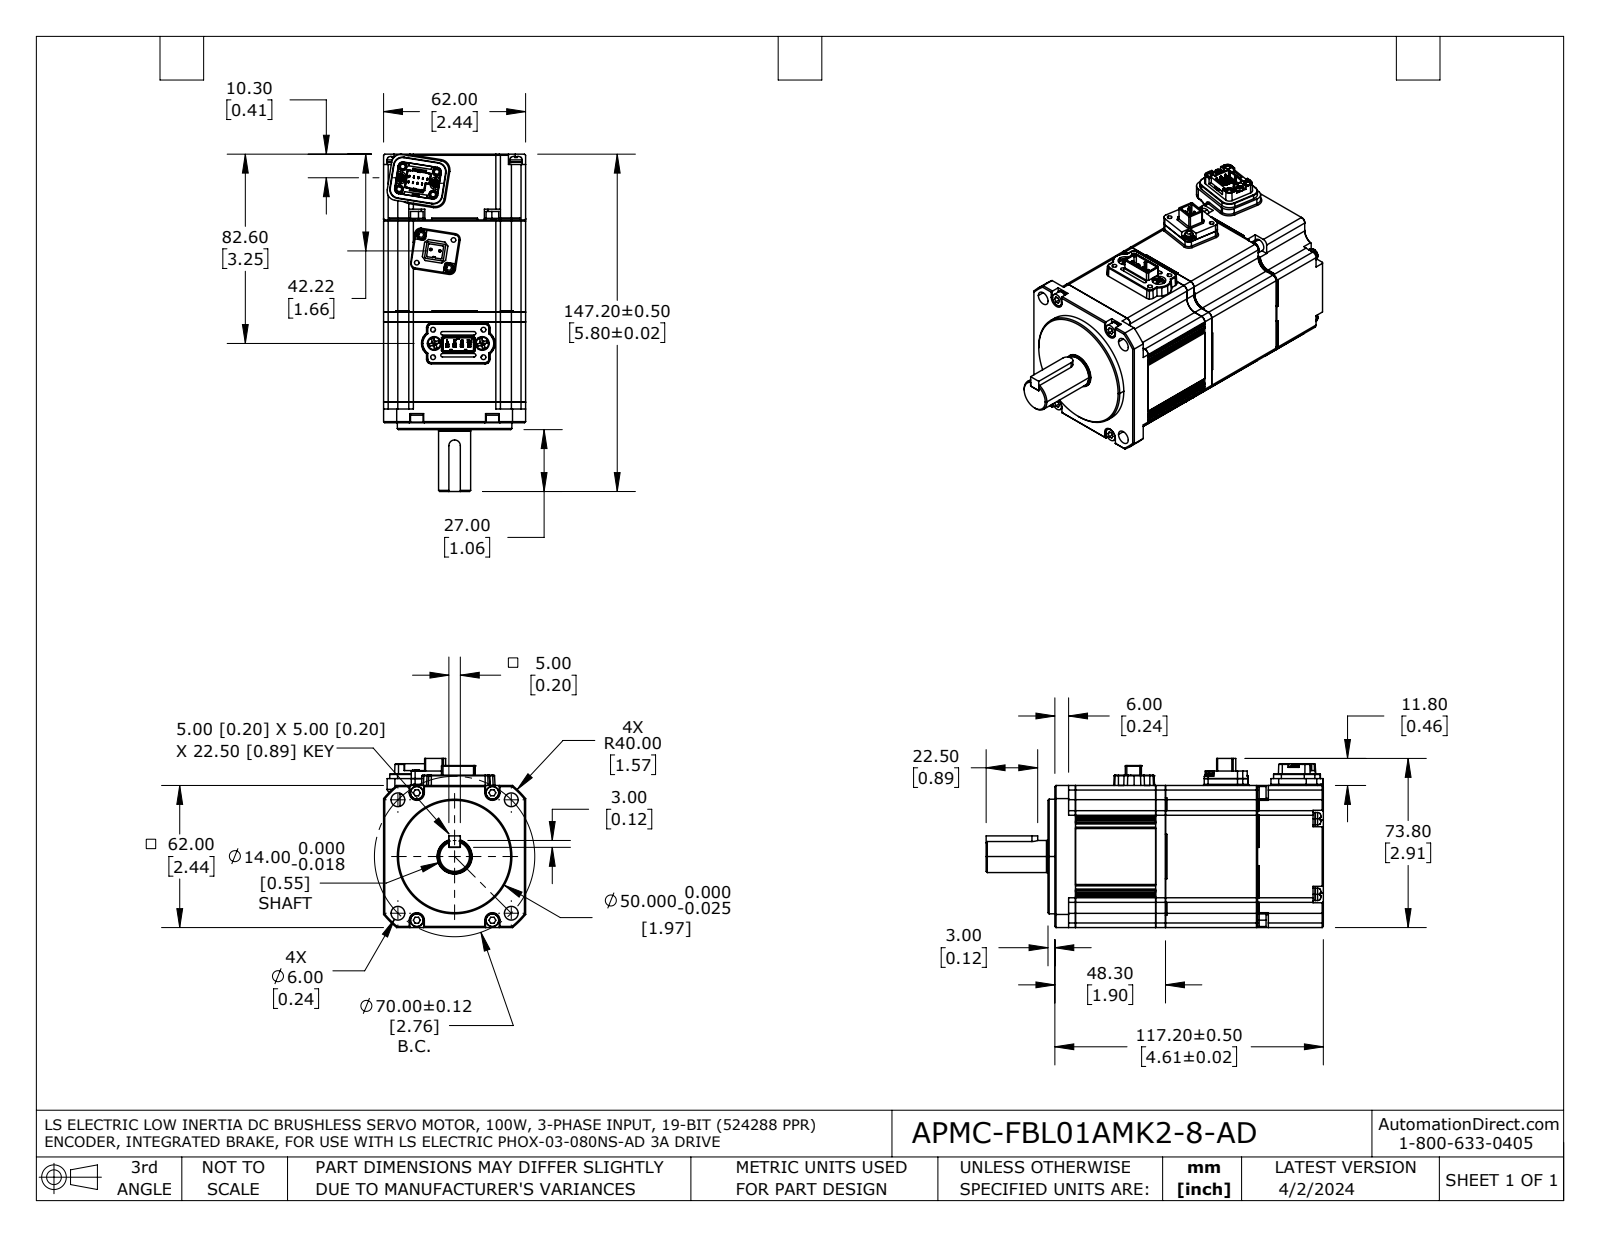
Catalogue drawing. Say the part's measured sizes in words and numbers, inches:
The part is named "APMC-FBL01AMK2-8-AD". Its 3-D file was written by "SolidWorks 2021 (AUTOMOTIVE_DESIGN)". It is 51 solids with 2196 faces: 1289 planar, 673 cylindrical and 234 other. Overall it measures 5.795 by 2.906 by 2.441 inches. Its volume is 25.14 cubic inches and its surface area 148.8 square inches. Round holes: 10 of diameter 0.083, 8 of diameter 0.138, 6 of diameter 0.118, 6 of diameter 0.236, 4 of diameter 0.079, 4 of diameter 0.122, 2 of diameter 0.039, 1 of diameter 0.13, 1 of diameter 0.134, 1 of diameter 0.512, 1 of diameter 0.602. Round bosses or shafts: 6 of diameter 0.213, 4 of diameter 0.22, 4 of diameter 0.217, 4 of diameter 0.118, 2 of diameter 0.165, 2 of diameter 0.142, 2 of diameter 0.138, 2 of diameter 0.087. Partial cylindrical surfaces (rounded edges, fillets, slot ends): 20 of radius 0.008, 20 of radius 0.012, 14 of radius 0.039, 12 of radius 0.079, 9 of radius 0.006, 8 of radius 0.118, 7 of radius 0.018, 6 of radius 0.004. The main face-to-face distances are 2.441, 0.169, 1.378, 0.02, 0.028, 1.547, 1.752, 1.583, 3.13, 1.61. The hole center spacings are 0.237, 0.335, 0.346, 0.602, 0.63, 0.879, 1.239, 1.273.
